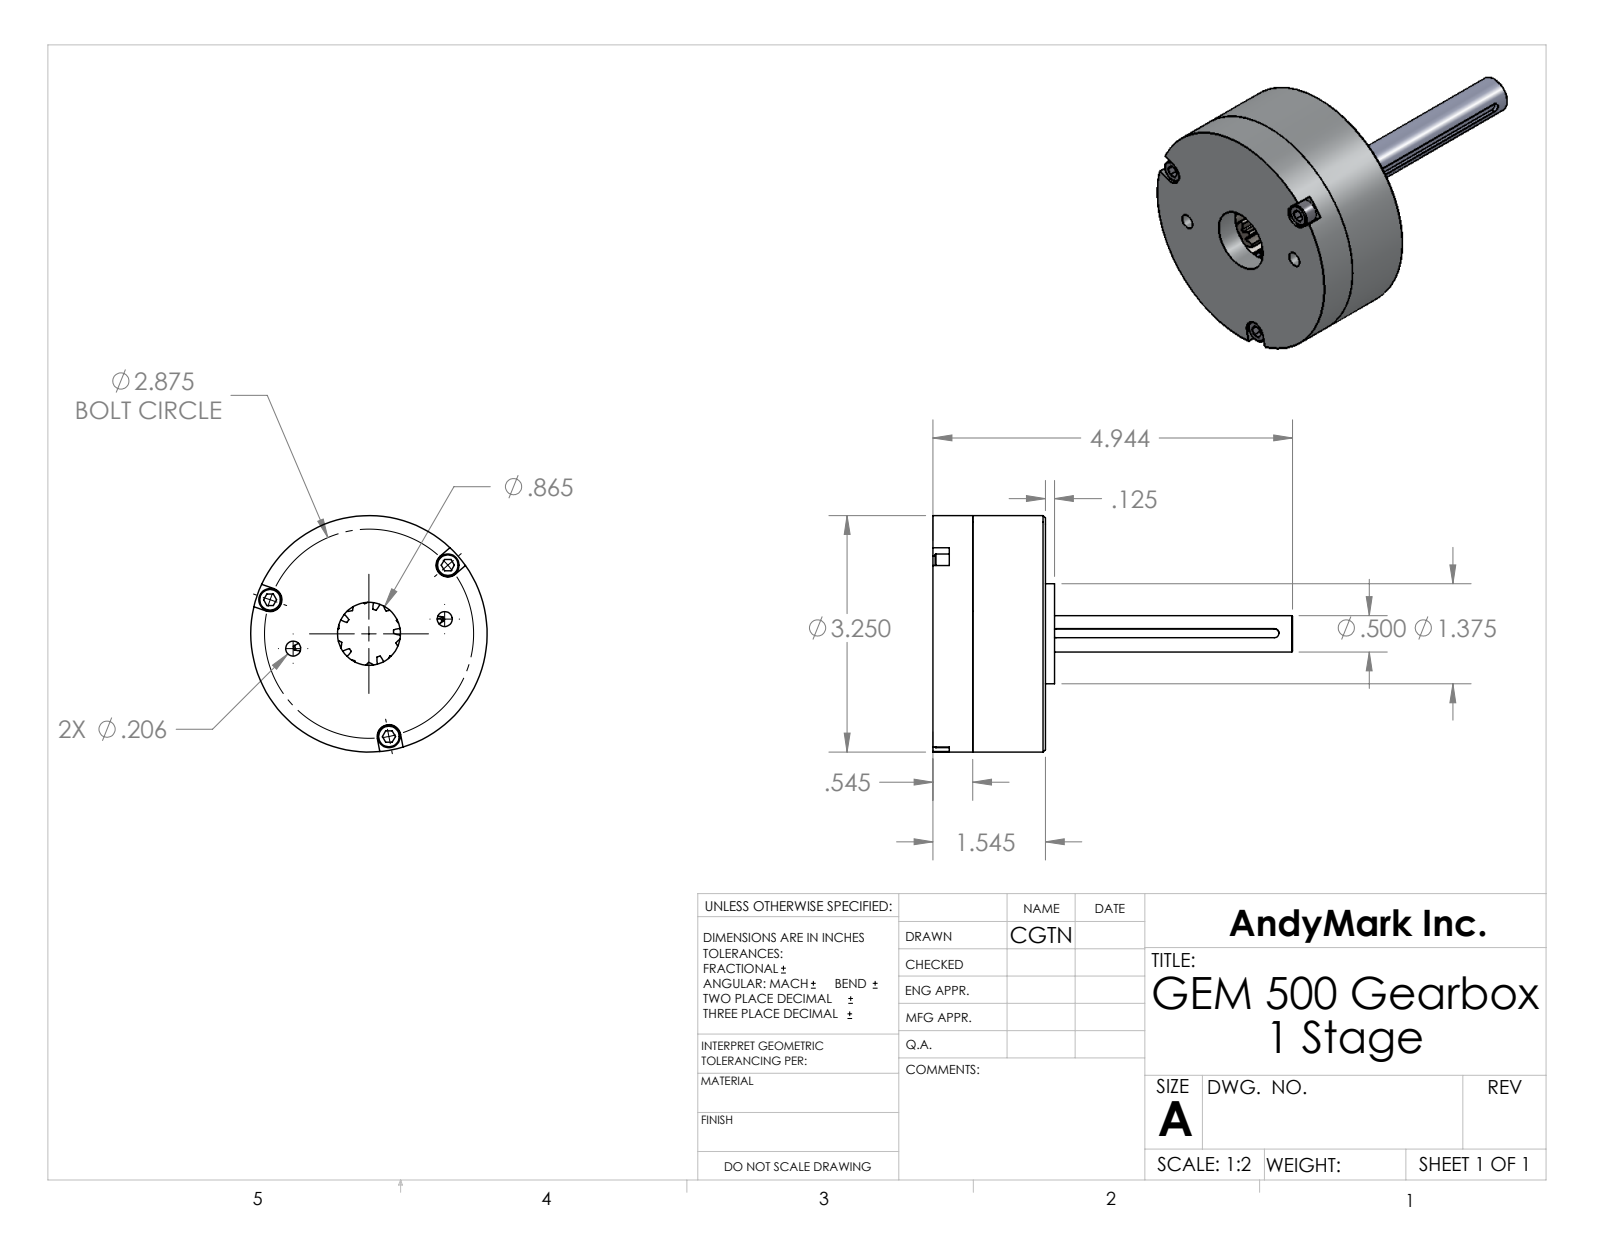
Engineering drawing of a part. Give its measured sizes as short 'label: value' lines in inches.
name: Output Shaft; GEM Spur Gear 12t; Spacer-Washer am-1065; GEM Gearbox 1 Stage (+8 more)
written by: SolidWorks 2010 (CONFIG_CONTROL_DESIGN)
unit: in
bodies: 22 solids, 784 faces (117 planar, 565 cylindrical, 102 other)
size: 4.944 × 3.25 × 3.25
volume: 12.09 in³; area: 103.5 in²
holes: 5× ⌀0.187, 5× ⌀0.188, 5× ⌀0.206, 4× ⌀0.196, 3× ⌀0.156, 2× ⌀0.33, 1× ⌀0.5, 1× ⌀0.635, 1× ⌀0.865, 1× ⌀1.125, 1× ⌀1.867, 1× ⌀2.063
bosses: 8× ⌀0.187, 5× ⌀0.313, 3× ⌀0.309, 1× ⌀3.25, 1× ⌀1.873, 1× ⌀1.625, 1× ⌀1.375, 1× ⌀1.125
rounds: 120× R0.309, 80× R0.522, 6× R0.125, 5× R0.237, 5× R0.238, 5× R0.35, 3× R0.162, 1× R0.062
face distances: 0.545, 1, 1.545, 0.831, 0.169, 0.714, 1.157, 0.326, 0.157, 0.388
hole spacings: 1.437, 0.687, 0.742, 1.438, 2.49, 1.307, 0.808, 0.808
